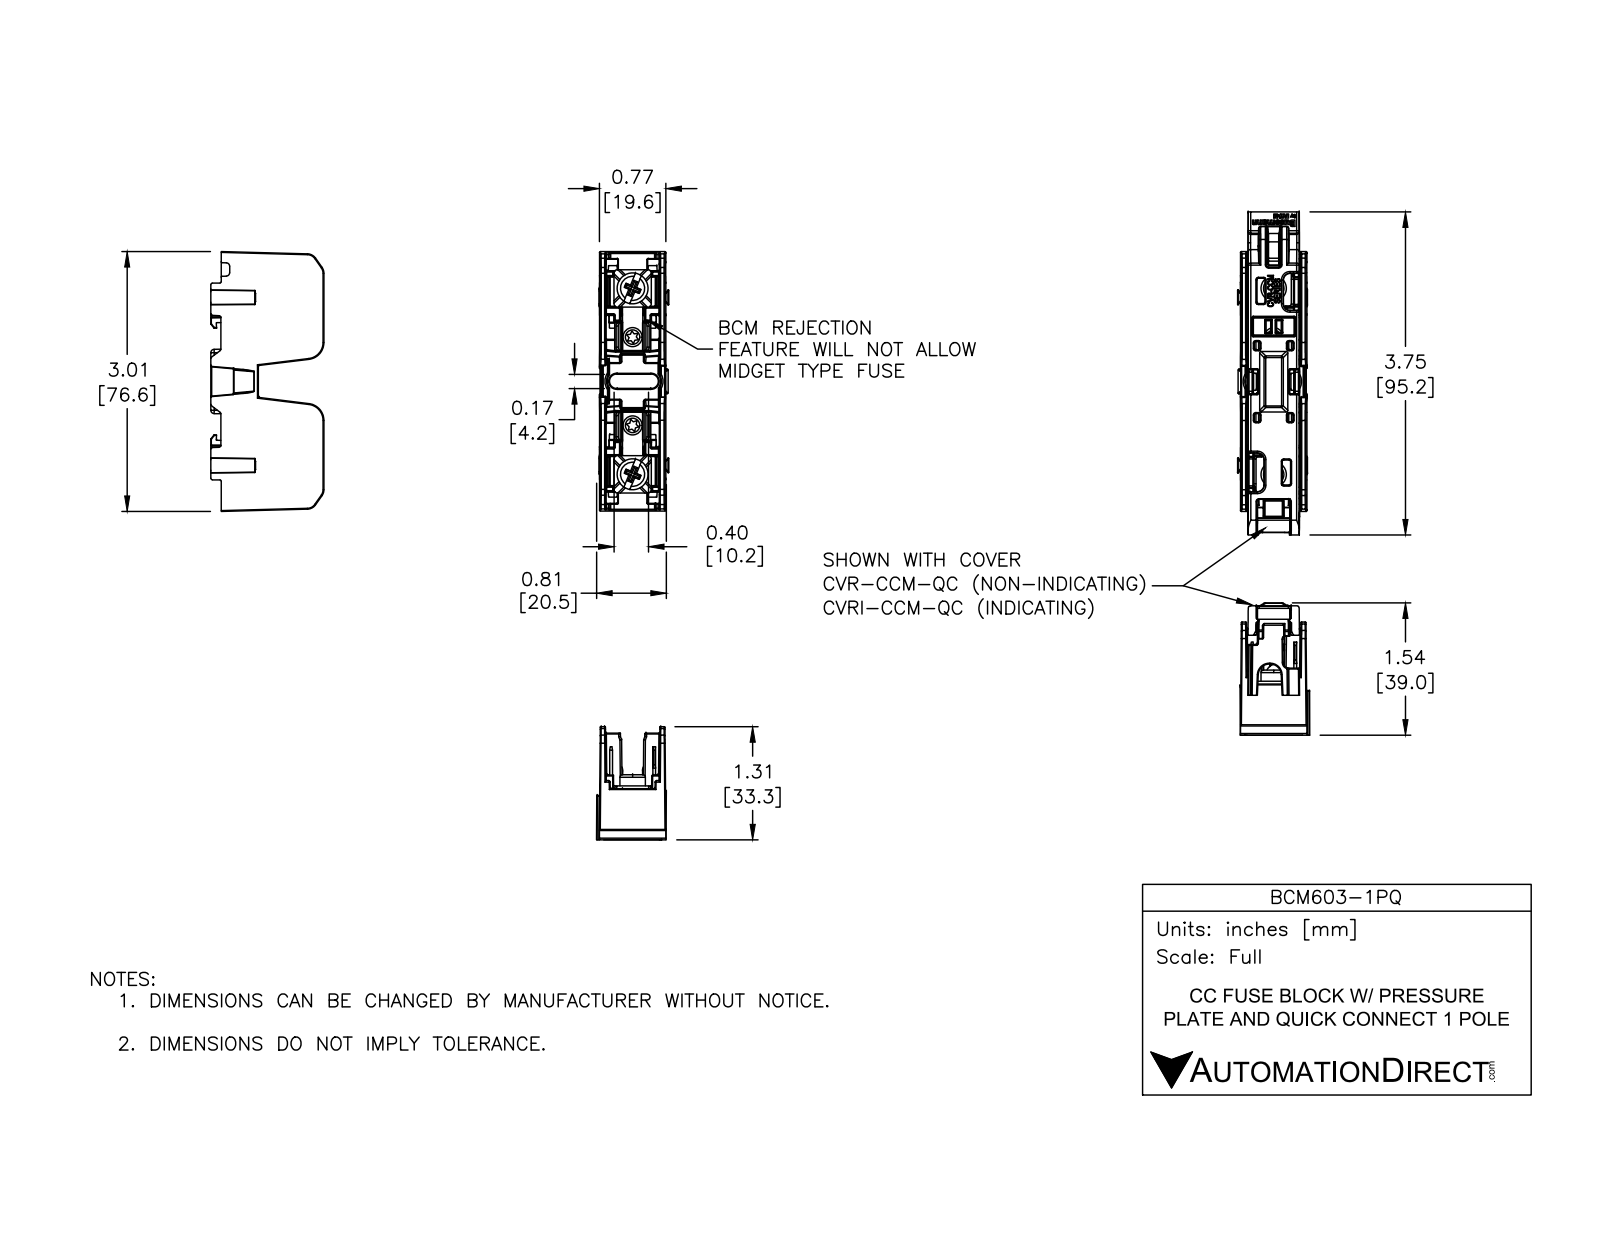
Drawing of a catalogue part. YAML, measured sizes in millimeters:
part_name: "BCM603-1PQ"
step_written_by: "SolidWorks 2021 (CONFIG_CONTROL_DESIGN)"
units: millimeters
bodies: {solids: 5, faces: 493, planar: 344, cylindrical: 95, other: 54}
overall_size: [76.6, 33.3, 20.6]
volume: 20400
surface_area: 16830
round_holes:
  - {diameter: 1.9, count: 4}
  - {diameter: 3.6, count: 2}
round_bosses_or_shafts:
  - {diameter: 7.5, count: 2}
  - {diameter: 5.6, count: 2}
  - {diameter: 3.5, count: 2}
partial_cylinders:
  - {radius: 0.1, count: 12}
  - {radius: 0.5, count: 12}
  - {radius: 0.3, count: 4}
  - {radius: 3, count: 4}
  - {radius: 0.8, count: 2}
  - {radius: 1.3, count: 2}
  - {radius: 1.5, count: 2}
  - {radius: 2.1, count: 2}
face_to_face_distances: [17.6, 17.6, 15.1, 0.8, 12, 14.9, 1.5, 3.1, 2.5, 27.6]
hole_center_spacings: [3, 56.7, 26, 53.9, 59.4]
